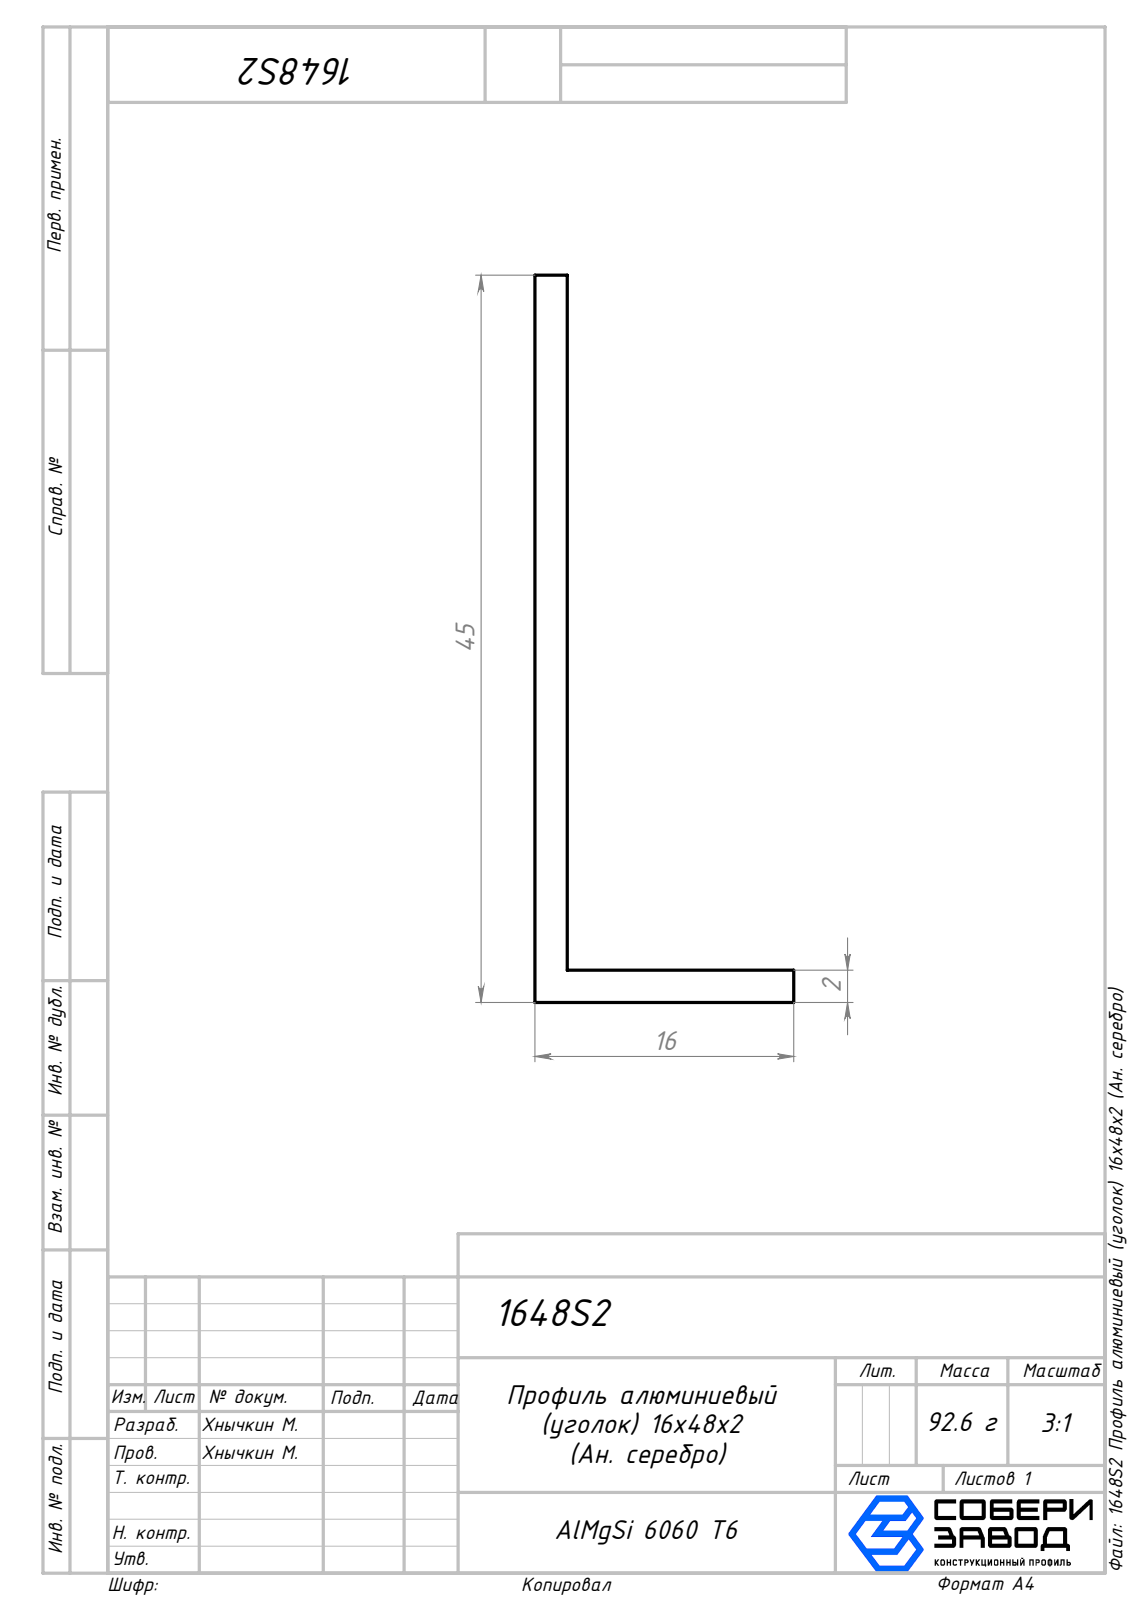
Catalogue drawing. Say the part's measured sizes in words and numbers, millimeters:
The part is named "1648S2 Профиль алюминиевый (уголок) 16х48х2 (Ан. серебро)". Its 3-D file was written by "SolidWorks 2026 (AUTOMOTIVE_DESIGN)". It is 1 solid with 8 faces: 8 planar, 0 cylindrical and 0 other. Overall it measures 100 by 45 by 16 millimeters. Its volume is 11 800 cubic millimeters and its surface area 12 436 square millimeters. The main face-to-face distances are 2, 16, 14, 45, 43, 100.
